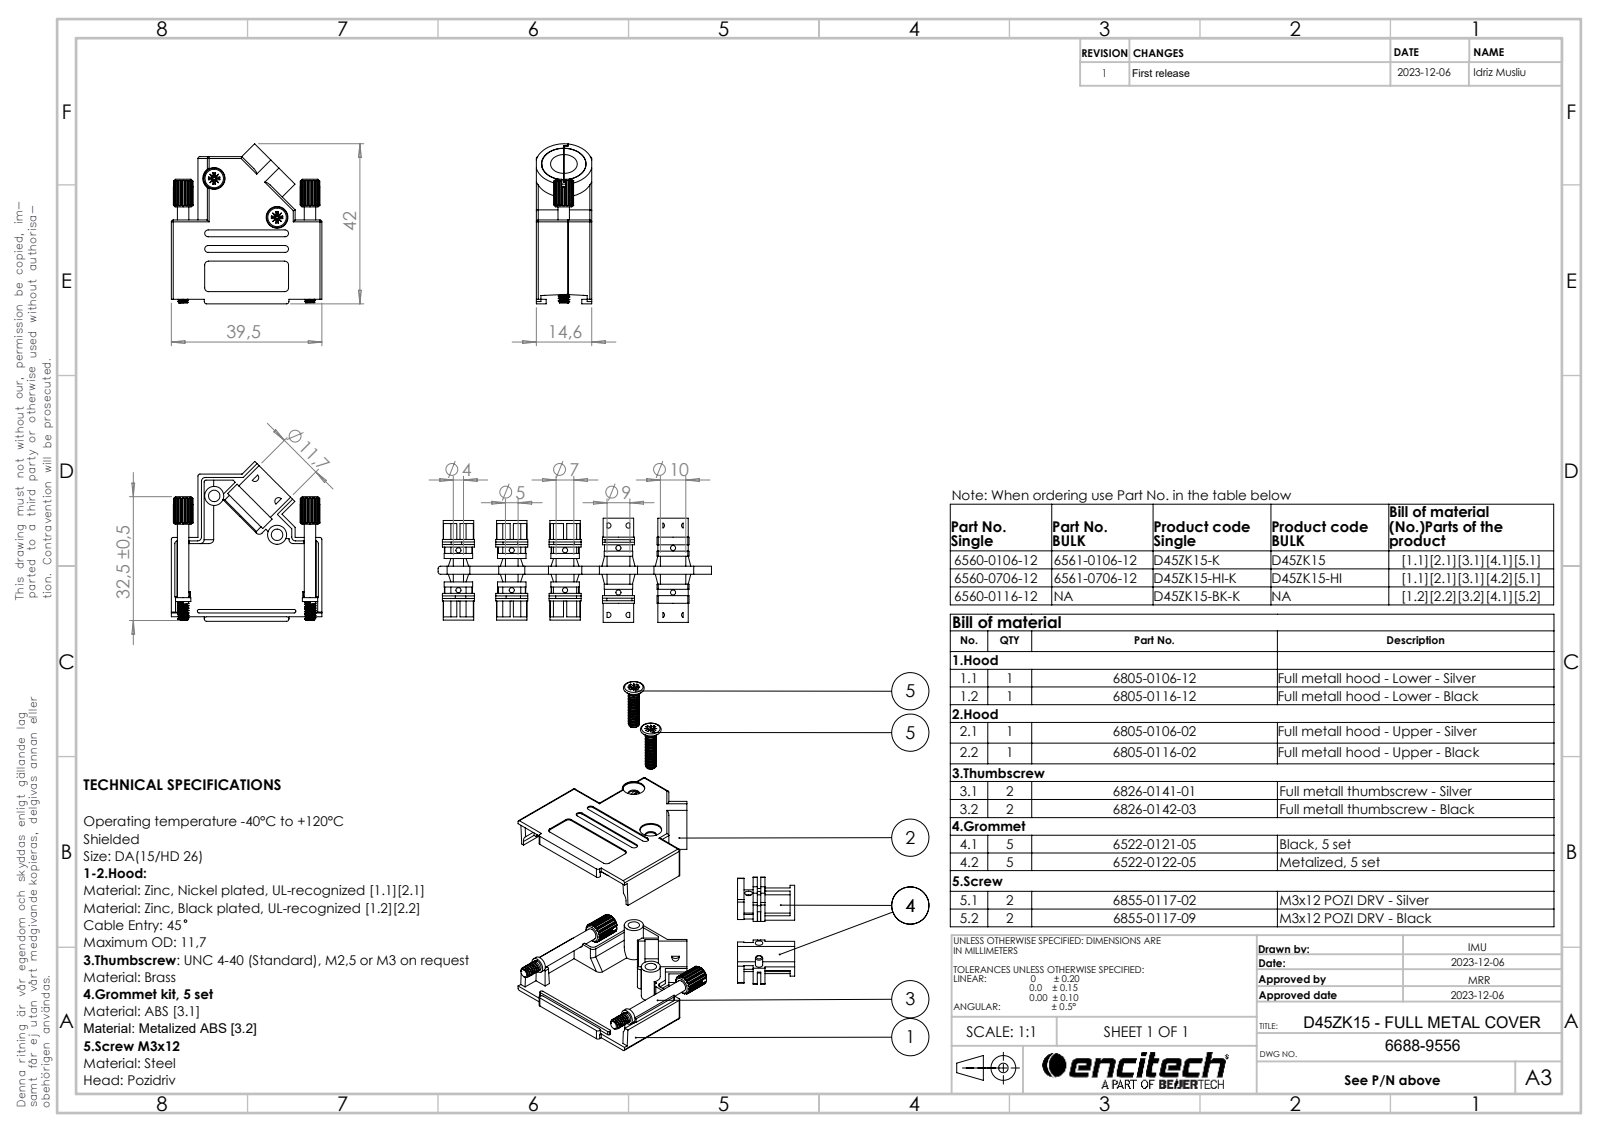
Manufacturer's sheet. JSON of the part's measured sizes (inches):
{"part_name": "6805-0106-12; 6522-0121-05 (7mm); 6688-9556; 6826-0141-01 (+2 more)", "step_written_by": "SolidWorks 2021 (AUTOMOTIVE_DESIGN)", "units": "inches", "bodies": {"solids": 8, "faces": 857, "planar": 452, "cylindrical": 330, "other": 75}, "overall_size": [1.654, 1.555, 0.573], "volume_in3": 0.424, "surface_area_in2": 18.29, "round_holes": [[0.079, 3], [0.118, 2], [0.224, 2], [0.276, 1], [0.461, 1]], "round_bosses_or_shafts": [[0.197, 2], [0.157, 2], [0.118, 2], [0.114, 2], [0.112, 2], [0.075, 2], [0.457, 1], [0.362, 1]], "partial_cylinders_radius": [[0.02, 28], [0.039, 19], [0.004, 8], [0.016, 6], [0.03, 4], [0.035, 4], [0.063, 4], [0.233, 4]], "face_to_face_distances": [0.047, 0.526, 0.573, 0.478, 0.035, 0.063, 0.561, 0.514, 1.492, 0.276], "hole_center_spacings": [0.225, 0.209, 0.229, 0.345, 0.394, 0.419, 0.564, 0.603]}
